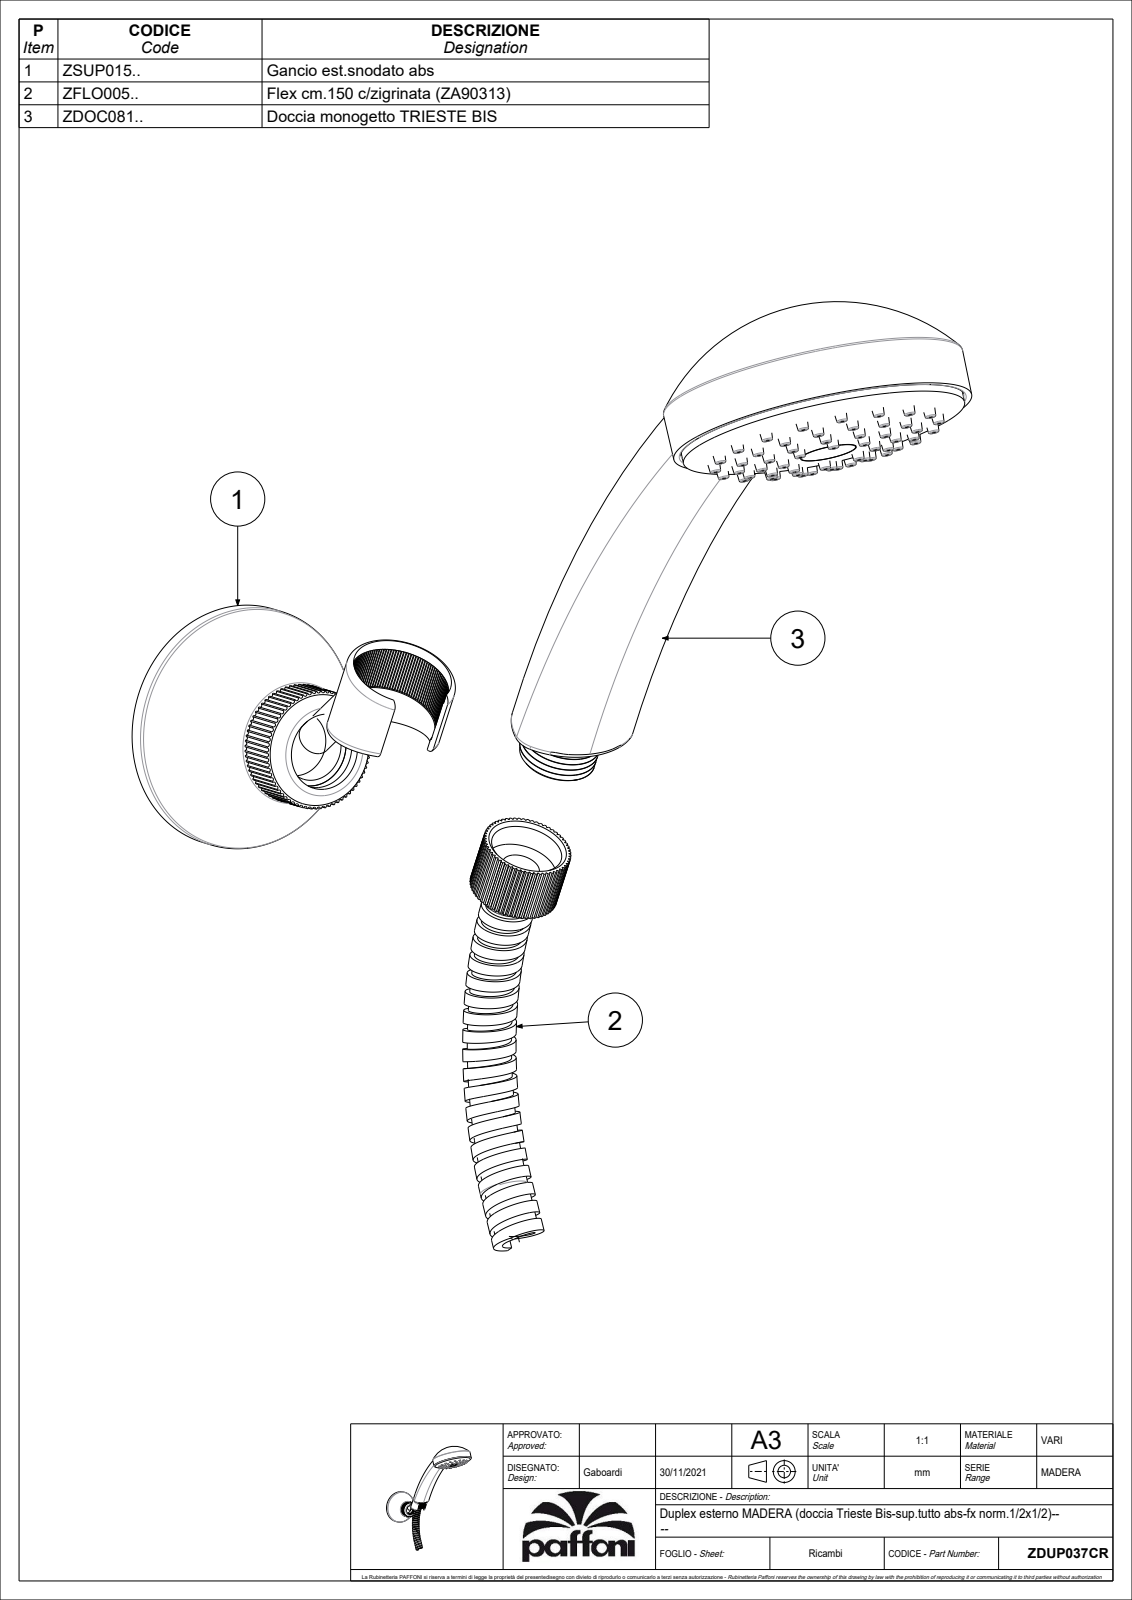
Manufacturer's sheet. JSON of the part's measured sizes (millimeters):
{"part_name": "ZDUP037CR", "step_written_by": "CREO PARAMETRIC BY PTC INC, 2020044 (CONFIG_CONTROL_DESIGN)", "units": "millimeters", "bodies": {"solids": 4, "faces": 1460, "planar": 462, "cylindrical": 516, "other": 482}, "overall_size": [258.2, 243.95, 80.3], "volume_mm3": 175837, "surface_area_mm2": 94093, "round_holes": [[19, 2], [3.25, 1], [3.31, 1], [4.5, 1], [6, 1], [9.63, 1], [10, 1], [12.83, 1], [13.2, 1], [14, 1], [15, 1], [17, 1]], "round_bosses_or_shafts": [[75.5, 1], [72.5, 1], [65.8, 1], [64, 1], [29.5, 1], [25, 1], [20.6, 1], [17.2, 1]], "partial_cylinders_radius": [[0.25, 95], [0.5, 84], [0.75, 16], [3.65, 2], [3.8, 2], [5, 2], [15.89, 2], [16.04, 2]], "face_to_face_distances": [7, 3, 21.5, 11.15, 10, 11, 8, 14, 11.5, 3.5], "hole_center_spacings": [24.85, 10.49, 10.5, 10.51, 14.35, 24.86]}
